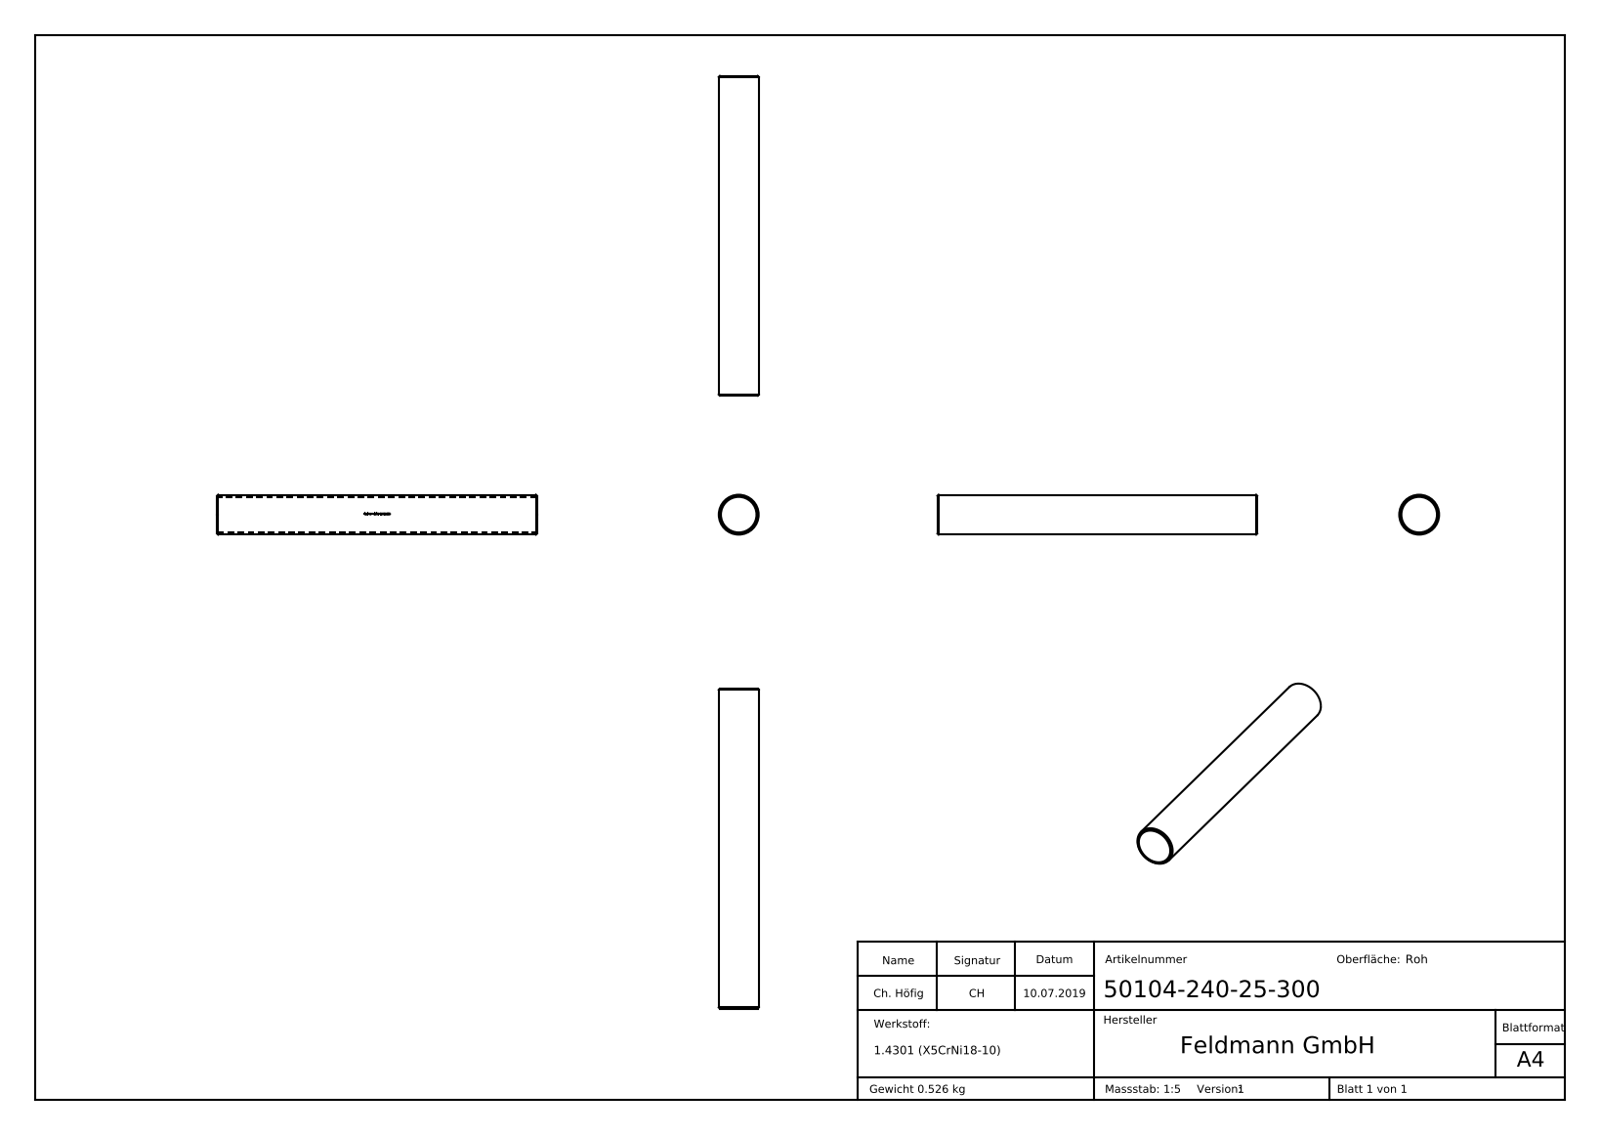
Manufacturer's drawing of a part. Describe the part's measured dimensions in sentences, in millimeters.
The part is named "50104-240-25-300". Its 3-D file was written by "SolidWorks 2015 (CONFIG_CONTROL_DESIGN)". It is 1 solid with 321 faces: 127 planar, 55 cylindrical and 139 other. Overall it measures 300 by 37.4 by 37.4 millimeters. Its volume is 66 611 cubic millimeters and its surface area 67 045 square millimeters. Round holes: 1 of diameter 33.4. Round bosses or shafts: 1 of diameter 37.4. Partial cylindrical surfaces (rounded edges, fillets, slot ends): 1 of radius 16.8. The main face-to-face distances are 300, 0.44, 0.88, 0.58, 9.72, 1.32, 2.02, 11.74, 2.14, 11.86.
